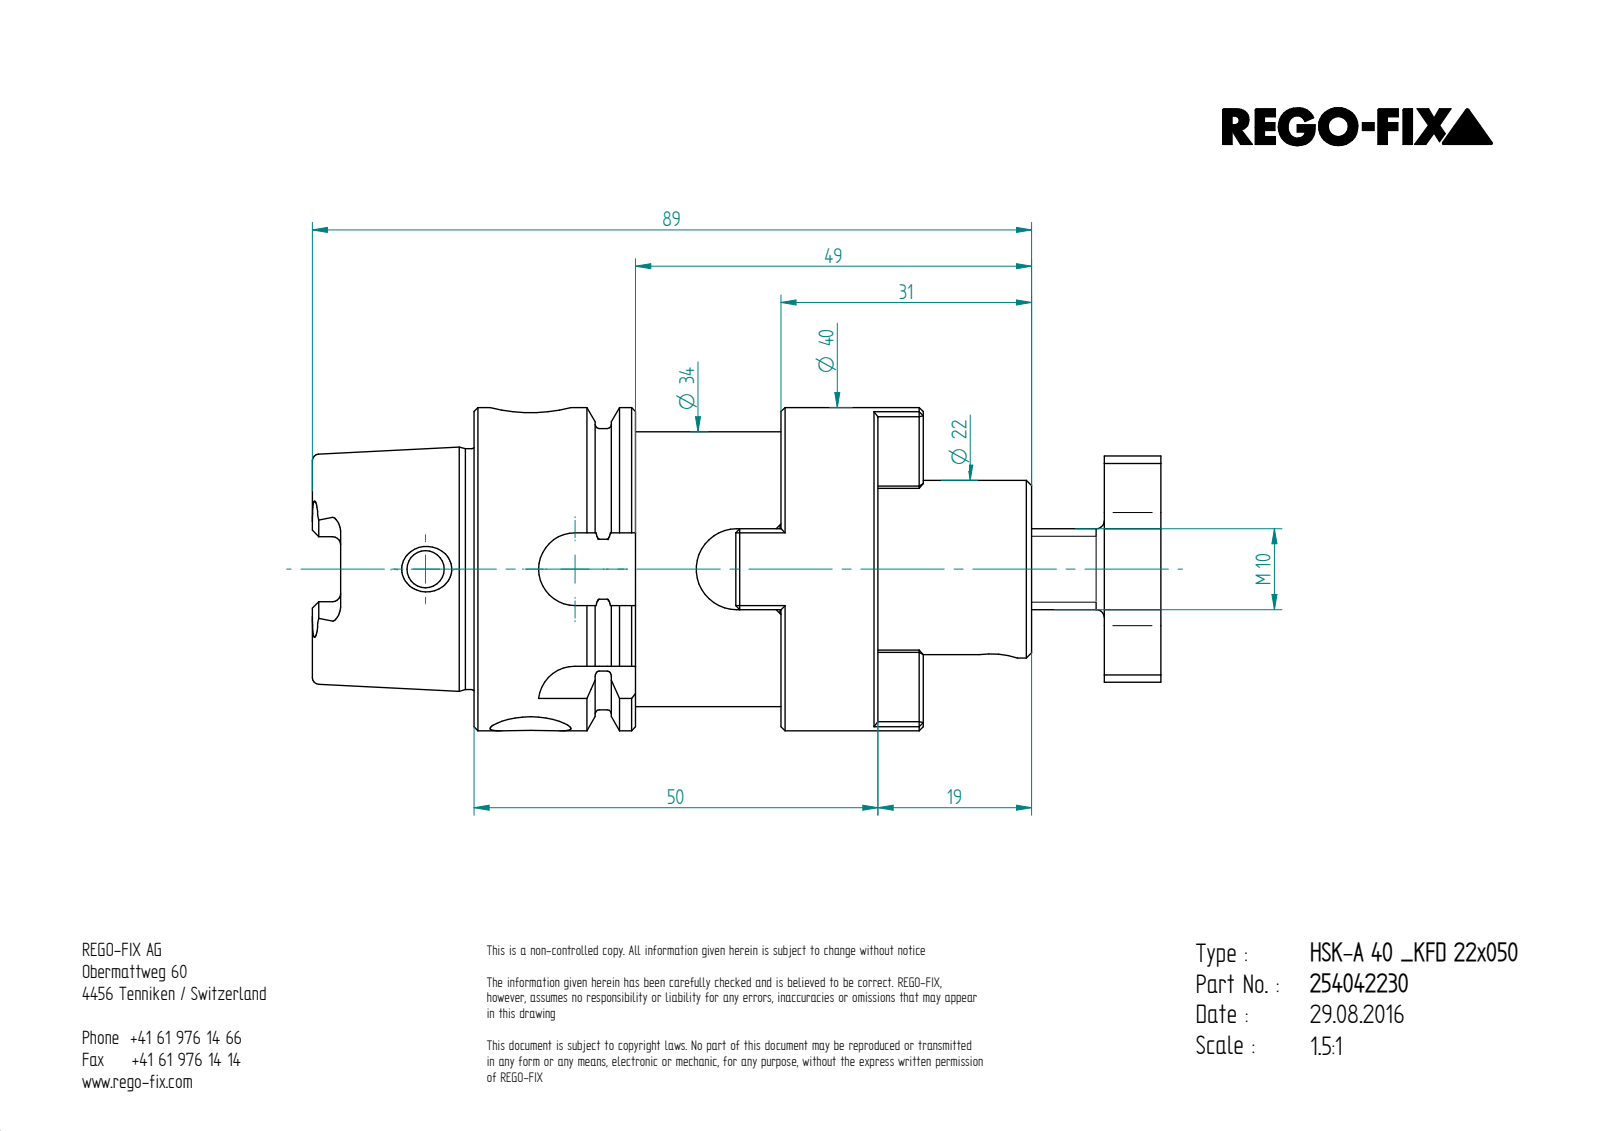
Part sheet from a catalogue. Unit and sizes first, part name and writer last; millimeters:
Units: millimetres
Overall size (bounding box): 89 × 40 × 40
Round holes (diameter × count): ⌀10 ×2, ⌀4.6 ×1, ⌀5 ×1, ⌀8.38 ×1, ⌀10.5 ×1, ⌀10.92 ×1, ⌀13 ×1, ⌀21 ×1, ⌀25.5 ×1
Round bosses / shafts (diameter × count): ⌀40 ×1, ⌀34.8 ×1, ⌀34 ×1, ⌀29.8 ×1, ⌀22 ×1, ⌀21.4 ×1
Partial cylindrical surfaces — rounded edges, fillets, slot ends (radius × count): R1 ×6, R1.88 ×4, R4.5 ×4, R3 ×2, R5 ×1
Main face-to-face distances: 20, 8, 38, 18, 30, 12, 31, 5.5, 28.5, 69
Volume: 48 580 mm³ · Surface area: 14 840 mm²
Bodies: 1 solid, 159 faces (63 planar, 41 cylindrical, 55 other)
STEP written by: Unknown (AUTOMOTIVE_DESIGN)
